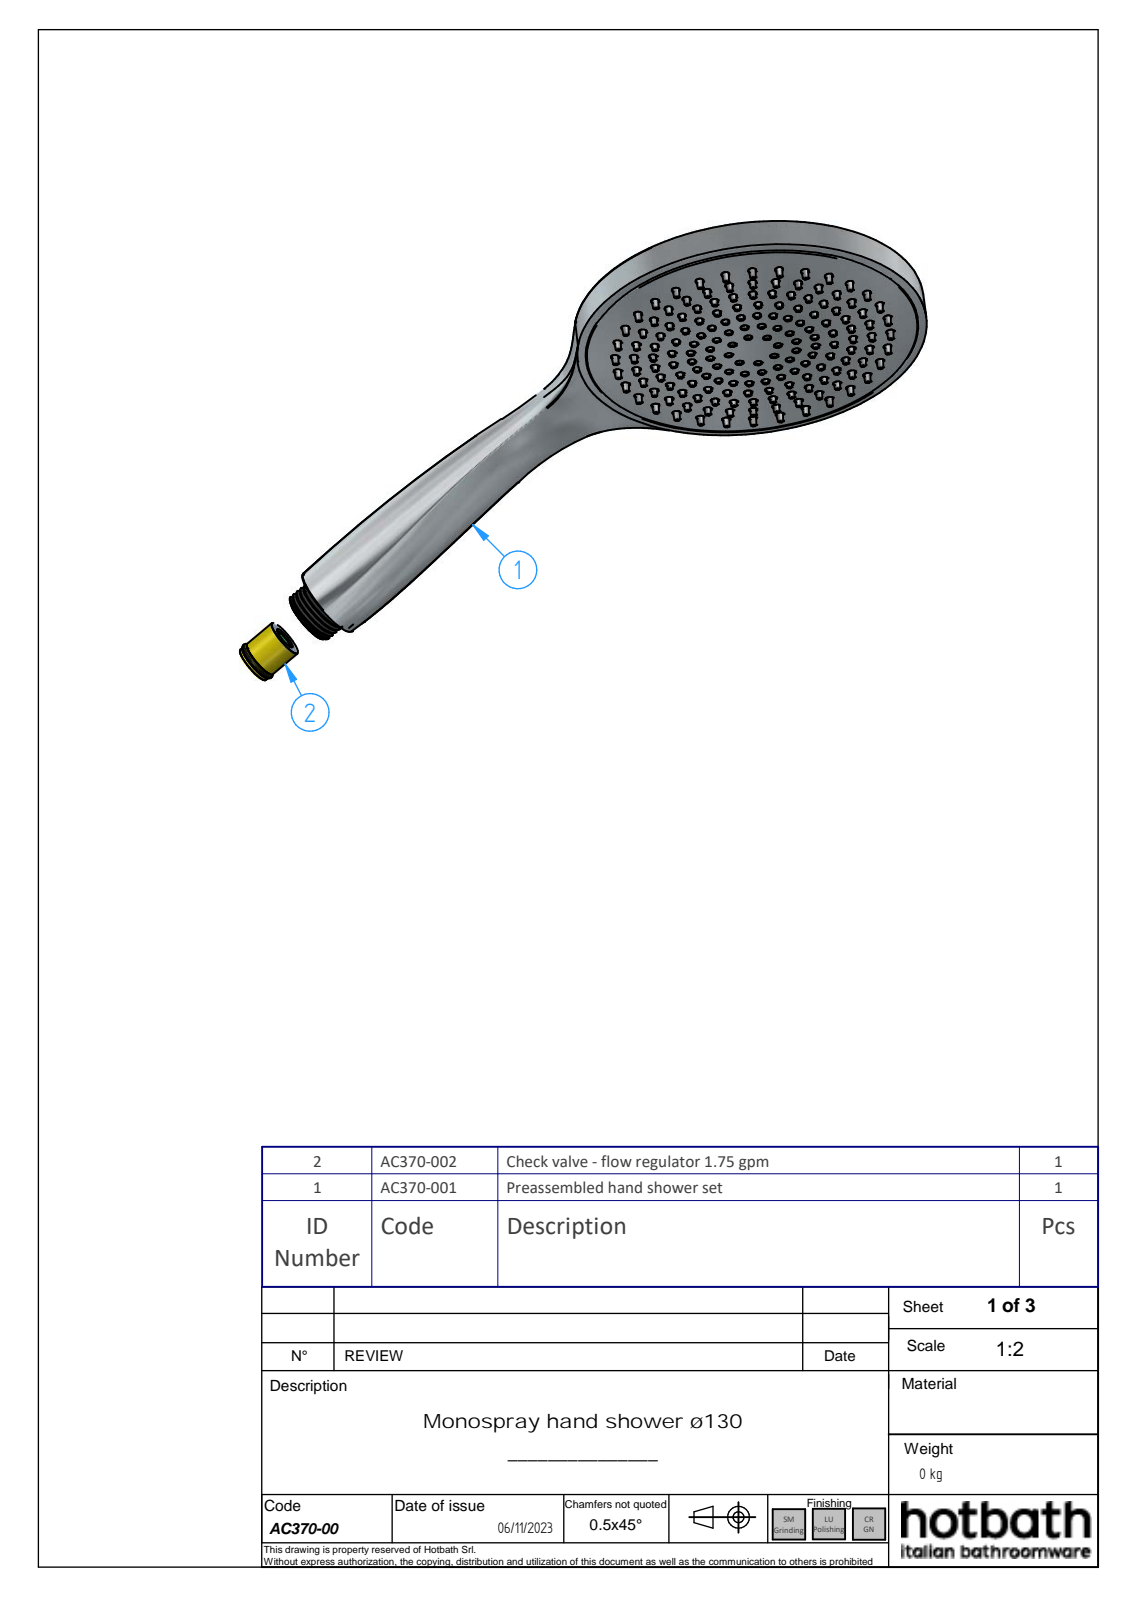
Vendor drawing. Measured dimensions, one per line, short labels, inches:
name: AC370-00; AC370-001_oa_0; A101051_00101ZZ; A040002_18136ZZ (+4 more)
written by: Solid Edge (AUTOMOTIVE_DESIGN)
unit: in
bodies: 5 solids, 4960 faces (972 planar, 1102 cylindrical, 2886 other)
size: 10.734 × 5.139 × 2.269
volume: 9.274 in³; area: 200.6 in²
holes: 12× ⌀0.091, 1× ⌀0.236, 1× ⌀0.394, 1× ⌀0.588, 1× ⌀4.614
bosses: 1× ⌀5.139, 1× ⌀4.764, 1× ⌀0.819, 1× ⌀0.752, 1× ⌀0.669
rounds: 64× R0.008, 59× R0.006, 54× R0.004, 31× R0.031, 23× R0.012, 17× R0.012, 14× R0.02, 12× R0.108
face distances: 0.079, 0.388, 0.309, 0.319, 0.126, 0.069, 0.197, 0.262, 0.183, 0.193
hole spacings: 2.274, 3.938, 1.177, 3.215, 4.393, 1.177, 2.273, 2.274
